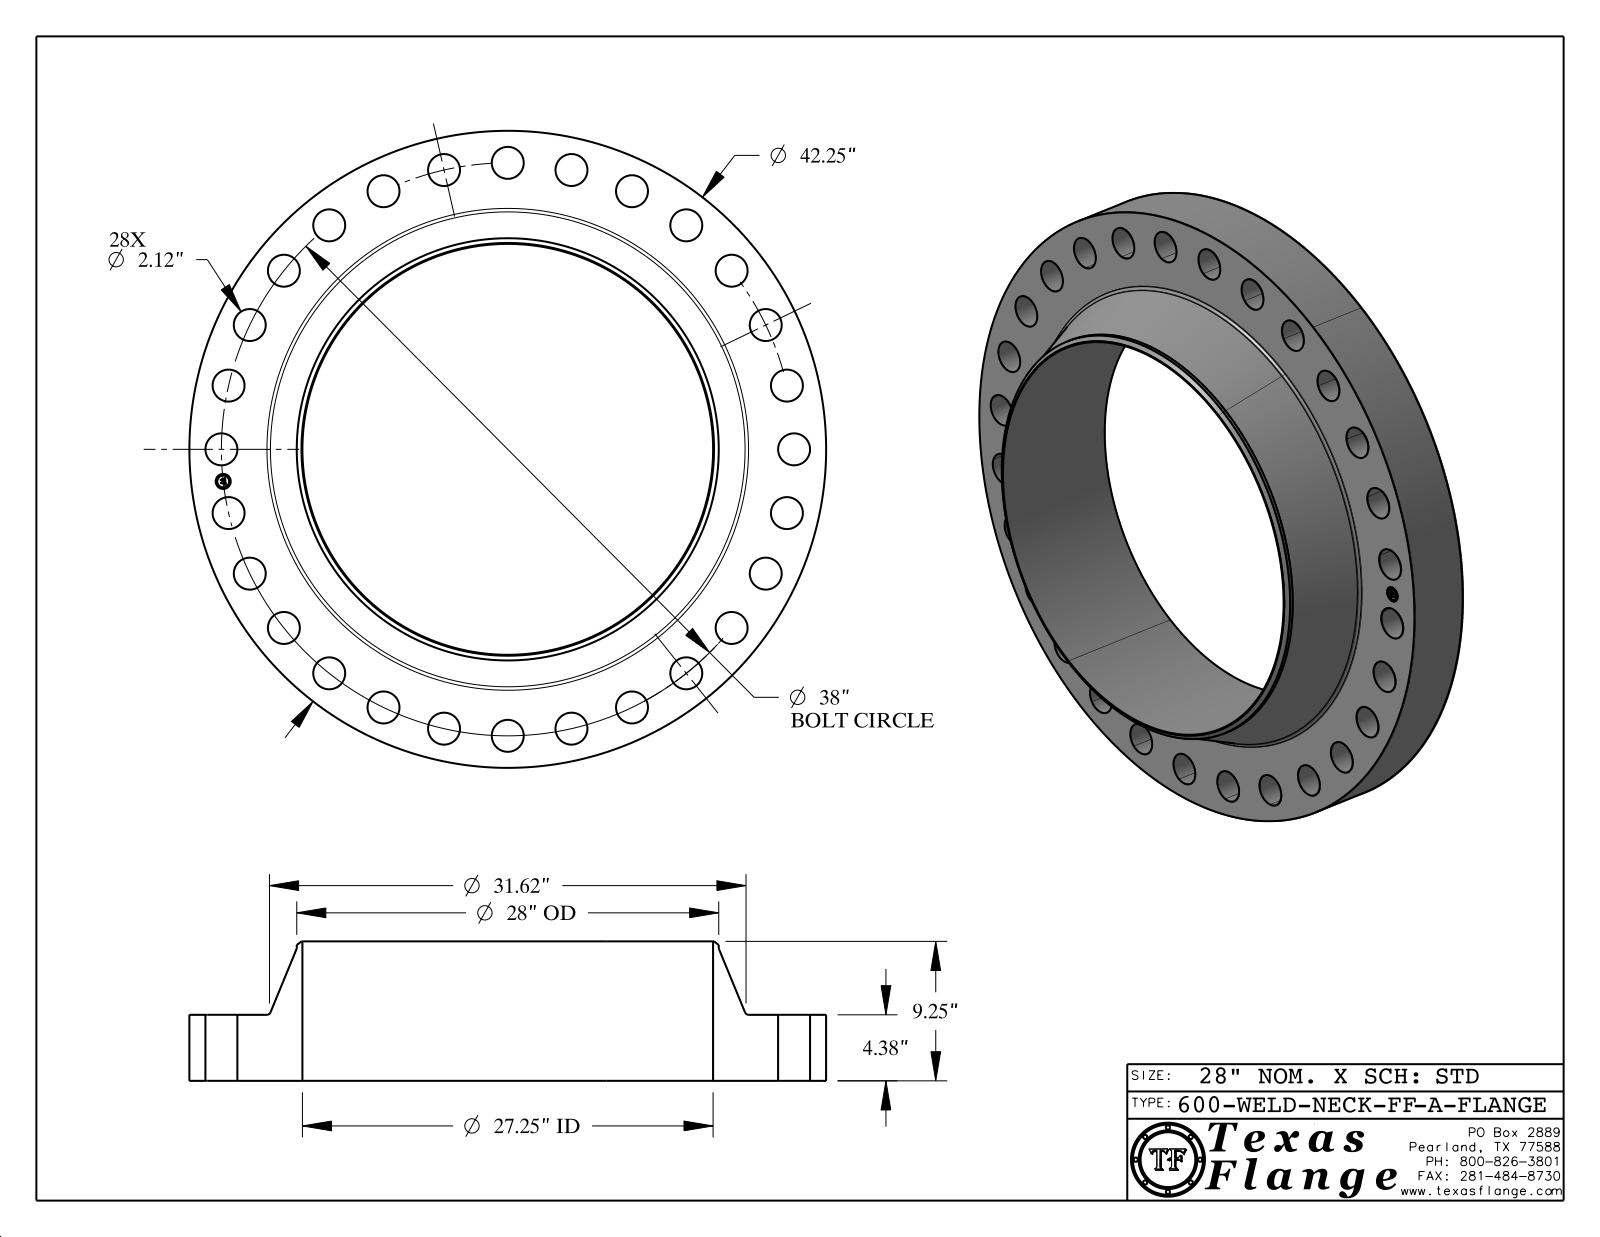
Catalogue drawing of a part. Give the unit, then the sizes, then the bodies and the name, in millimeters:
Units: millimetres
Overall size (bounding box): 1073.2 × 1073.2 × 235
Round holes (diameter × count): ⌀53.8 ×28, ⌀25.4 ×1, ⌀692.2 ×1
Round bosses / shafts (diameter × count): ⌀1.5 ×8, ⌀1073.2 ×1, ⌀711.2 ×1, ⌀20 ×1
Main face-to-face distances: 111.3, 235, 123.7, 110.9, 0.4, 124.1, 7.6, 7.4, 1.4, 4.9
Hole centre spacings: 482.6, 513.5, 682.5, 817.3, 911, 941, 959.1, 214.8
Volume: 60 210 000 mm³ · Surface area: 2 535 000 mm²
Bodies: 1 solid, 456 faces (368 planar, 82 cylindrical, 6 other)
Part name (STEP PRODUCT): 600-WELD-NECK-FF, Series A
STEP written by: CATIA V5 STEP AP214 (AUTOMOTIVE_DESIGN)
